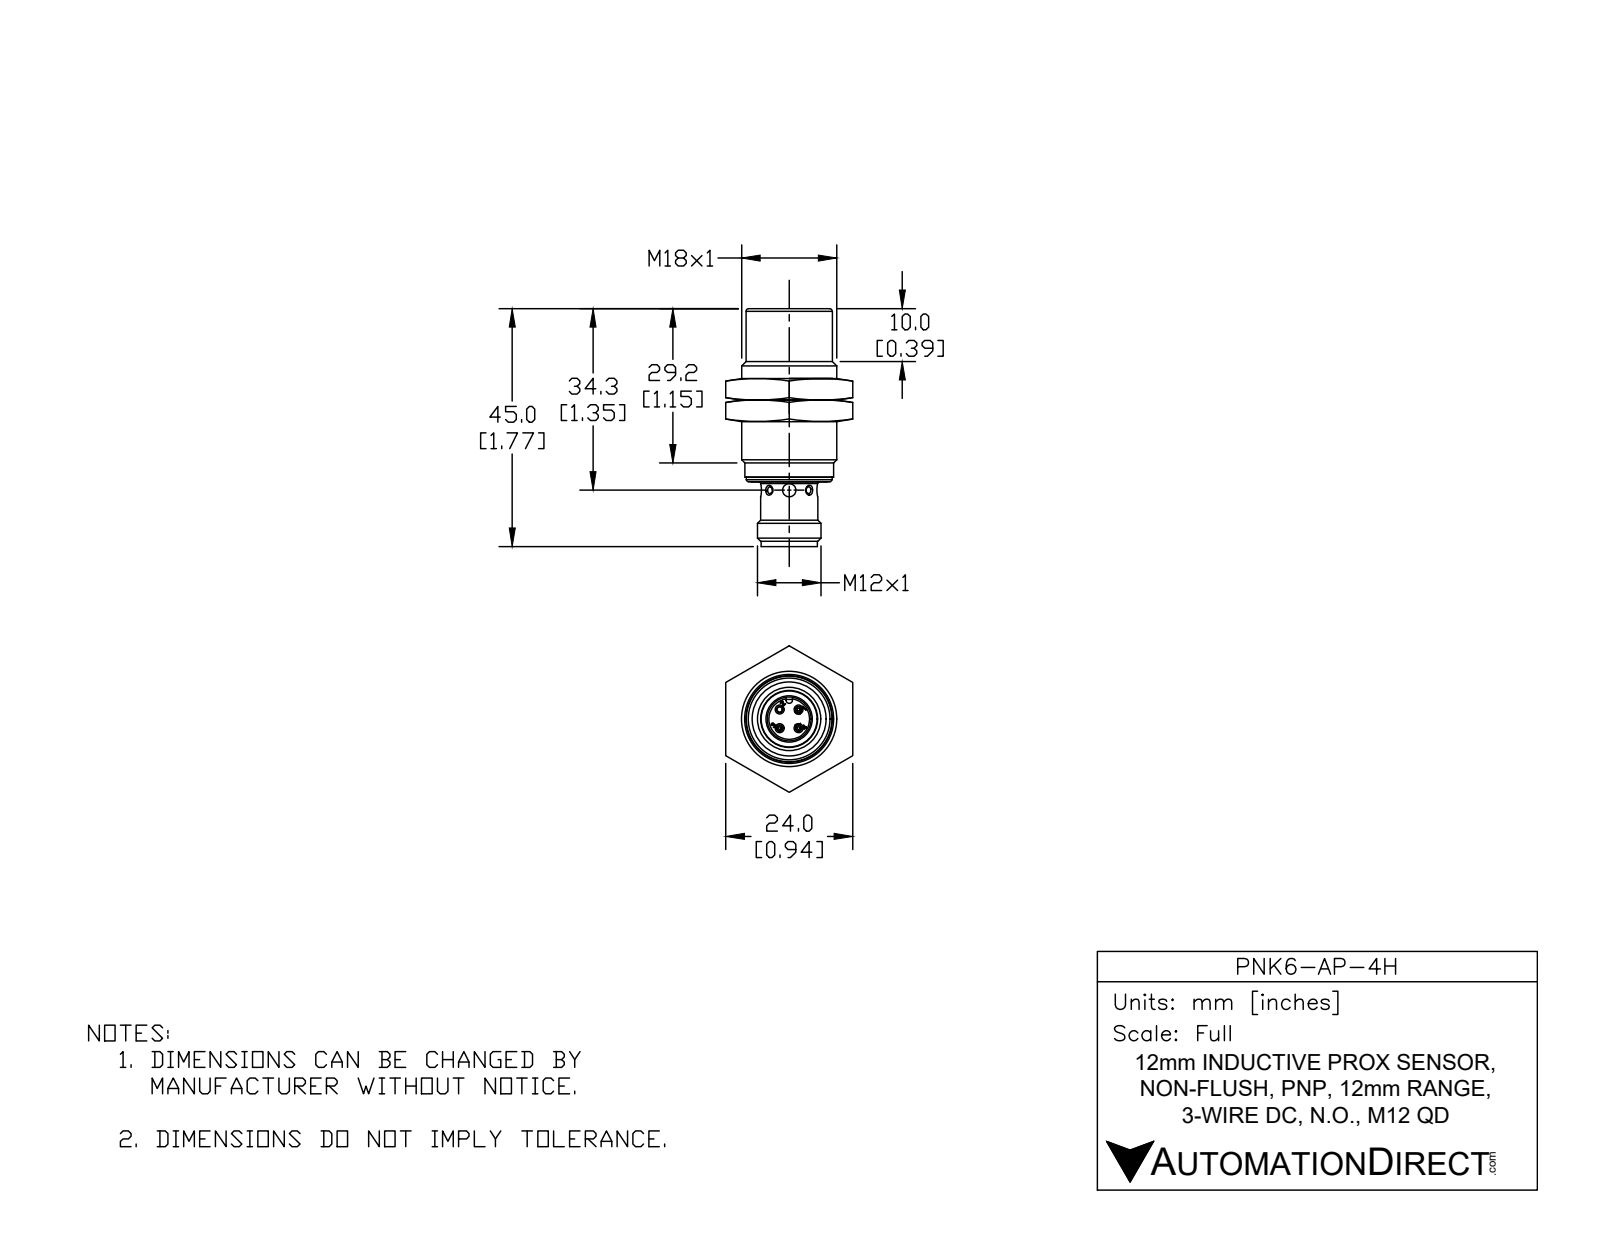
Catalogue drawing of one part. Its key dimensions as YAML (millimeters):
part_name: "PNK6-AP-4H"
step_written_by: "SolidWorks 2017 (AUTOMOTIVE_DESIGN)"
units: millimeters
bodies: {solids: 1, faces: 476, planar: 118, cylindrical: 129, other: 229}
overall_size: [45, 18, 18]
volume: 6570
surface_area: 4930
round_holes:
  - {diameter: 1, count: 3}
  - {diameter: 1.1, count: 3}
  - {diameter: 2.5, count: 2}
  - {diameter: 1, count: 1}
  - {diameter: 8.2, count: 1}
  - {diameter: 8.3, count: 1}
  - {diameter: 10, count: 1}
  - {diameter: 15.7, count: 1}
round_bosses_or_shafts:
  - {diameter: 1, count: 9}
  - {diameter: 18, count: 1}
  - {diameter: 16.8, count: 1}
  - {diameter: 16.3, count: 1}
  - {diameter: 16.2, count: 1}
  - {diameter: 15.6, count: 1}
  - {diameter: 12, count: 1}
  - {diameter: 10.8, count: 1}
partial_cylinders:
  - {radius: 0.1, count: 24}
  - {radius: 1, count: 6}
  - {radius: 1.8, count: 6}
  - {radius: 0.6, count: 1}
  - {radius: 0.8, count: 1}
face_to_face_distances: [11.5, 0.8, 10.7, 31.4, 30.7, 19.9, 32.8, 1.4, 32.1, 21.3]
hole_center_spacings: [2.5, 3.5, 5]
